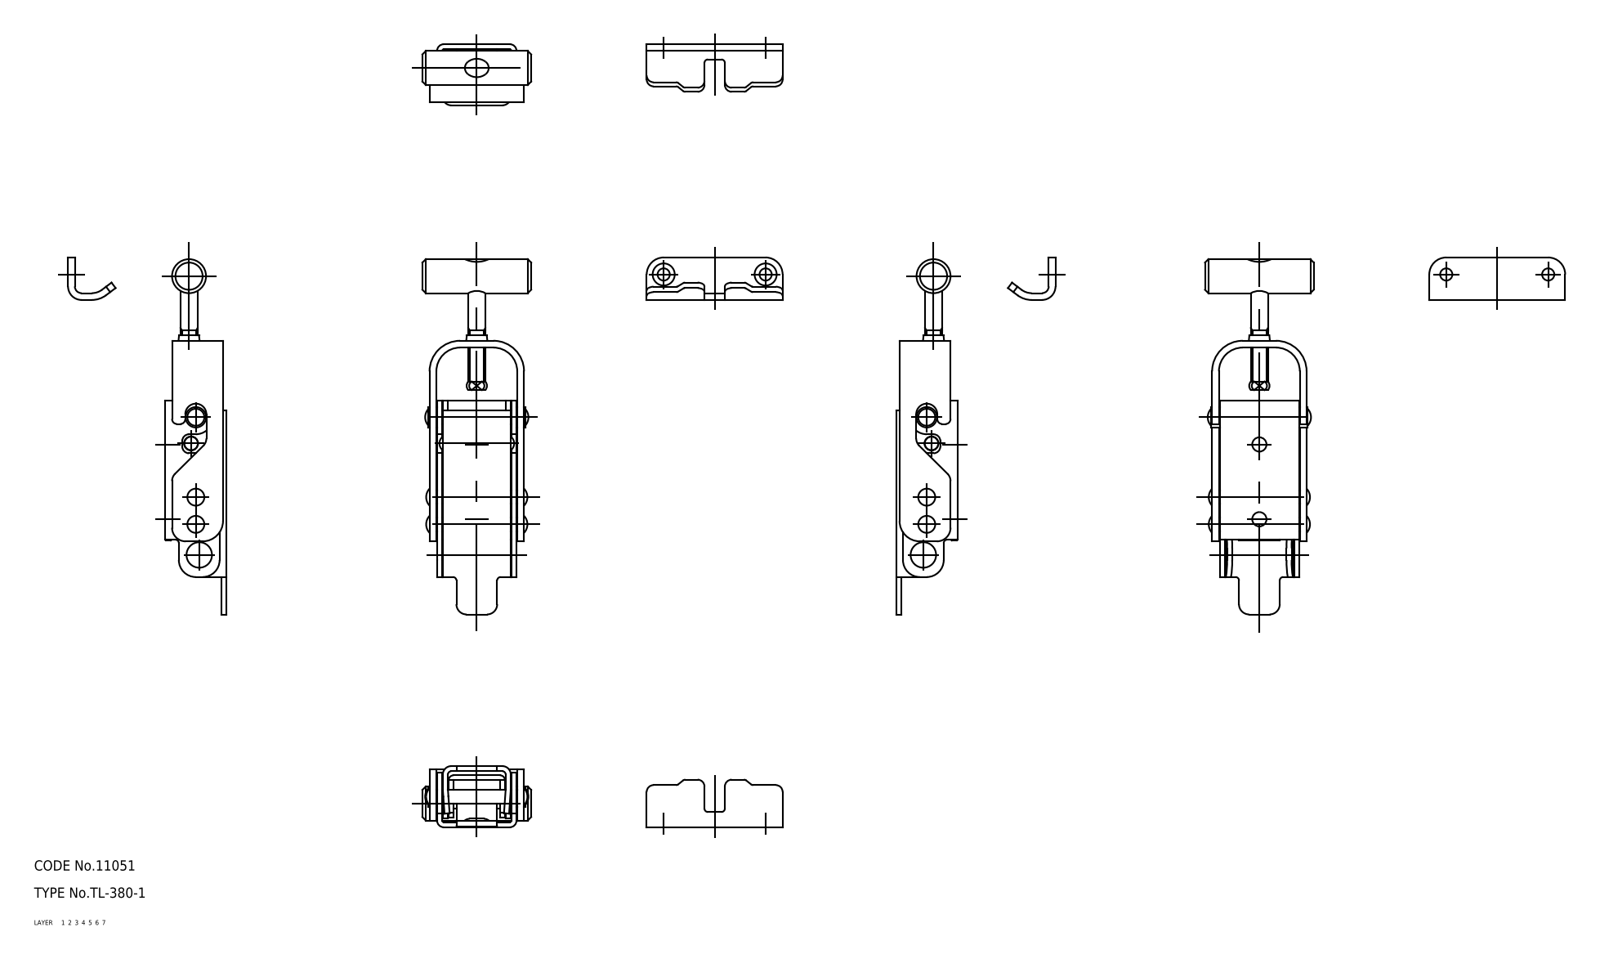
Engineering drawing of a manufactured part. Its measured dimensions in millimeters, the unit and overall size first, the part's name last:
Units: millimetres
Overall size (bounding box): 105 × 40 × 18
Volume: 15 853 mm³ · Surface area: 18 929 mm²
Bodies: 4 solids, 309 faces (0 planar, 0 cylindrical, 309 other)
Part name (STEP PRODUCT): 67125148; 67125161; 67125174; 67125187
STEP written by: CADfix (AUTOMOTIVE_DESIGN)
